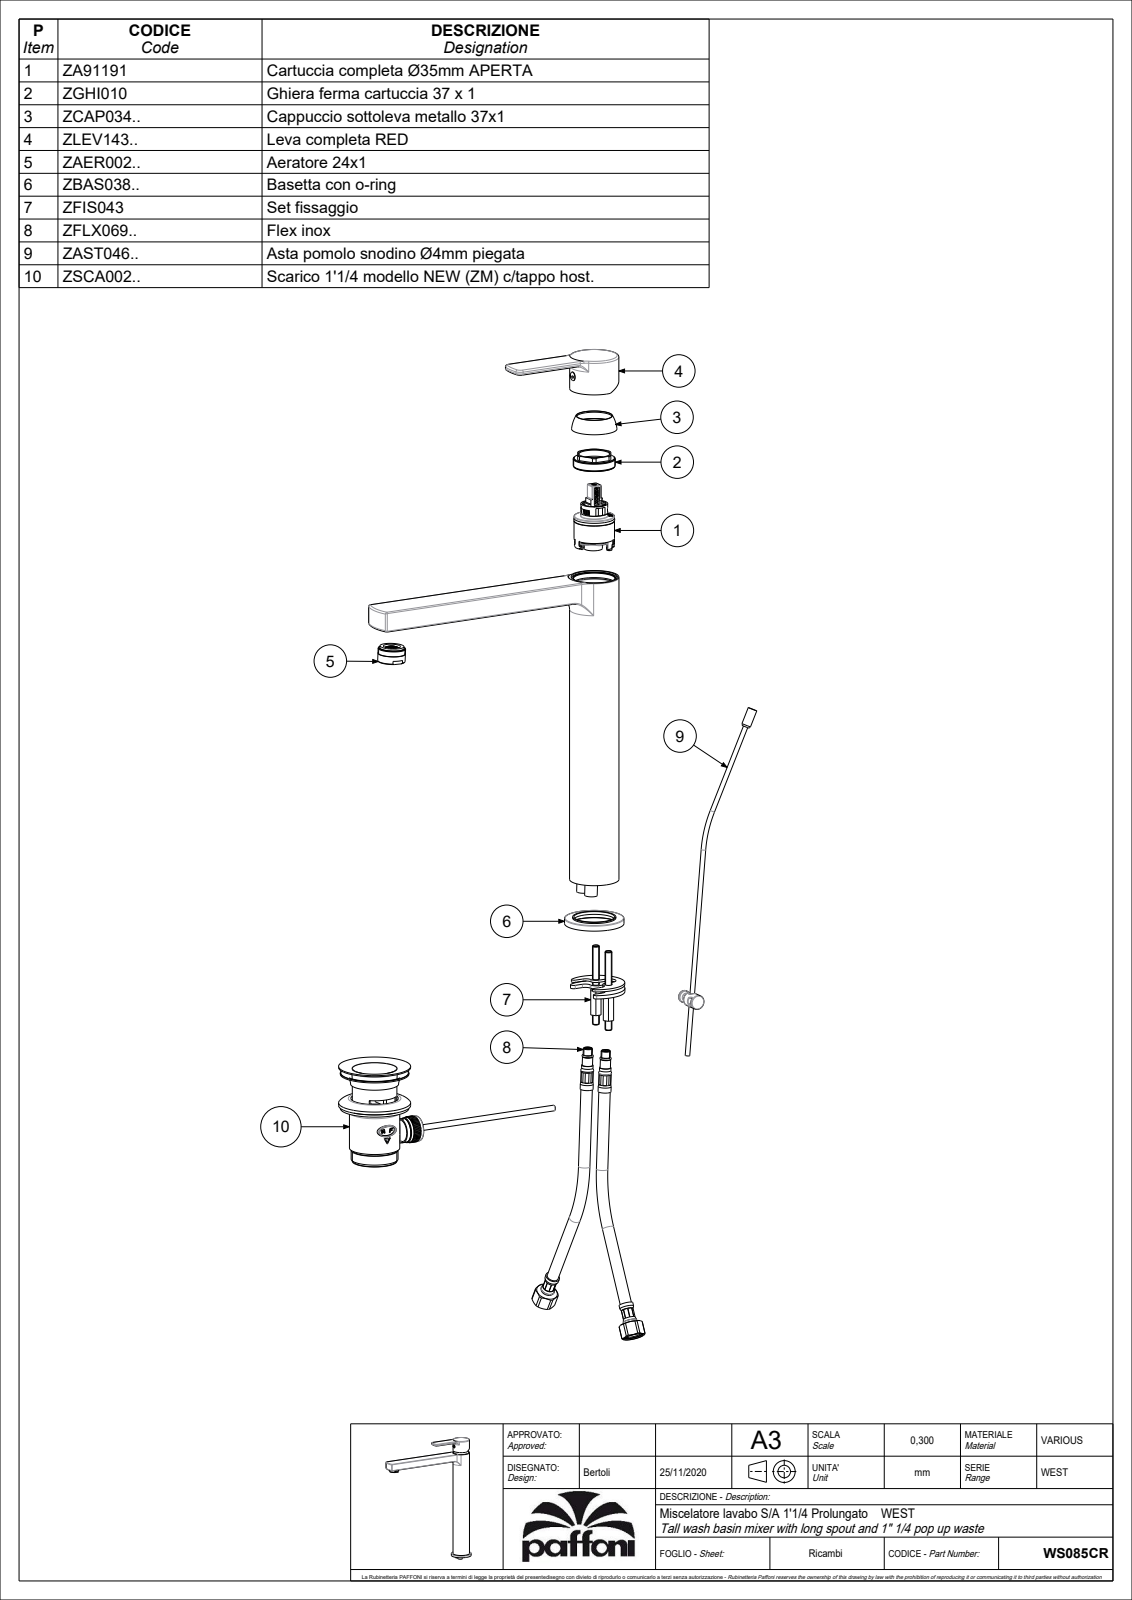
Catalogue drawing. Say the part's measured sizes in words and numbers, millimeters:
The part is named "WS085CR". Its 3-D file was written by "CREO PARAMETRIC BY PTC INC, 2020044 (CONFIG_CONTROL_DESIGN)". It is 7 solids with 3431 faces: 2429 planar, 557 cylindrical and 445 other. Overall it measures 314.78 by 263.5 by 52 millimeters. Its volume is 258 971 cubic millimeters and its surface area 171 608 square millimeters. Round holes: 4 of diameter 6, 3 of diameter 4, 3 of diameter 5, 2 of diameter 5.5, 2 of diameter 6.5, 2 of diameter 8, 2 of diameter 8.2, 1 of diameter 3, 1 of diameter 3.3, 1 of diameter 3.4, 1 of diameter 3.5, 1 of diameter 4.5. Round bosses or shafts: 7 of diameter 8, 3 of diameter 4, 2 of diameter 6, 2 of diameter 4.8, 1 of diameter 52, 1 of diameter 43.2, 1 of diameter 43, 1 of diameter 42.6. Partial cylindrical surfaces (rounded edges, fillets, slot ends): 85 of radius 0.5, 25 of radius 1.5, 17 of radius 1, 6 of radius 1.7, 5 of radius 2, 4 of radius 0.8, 4 of radius 5.8, 3 of radius 12.75. The main face-to-face distances are 3.5, 14.5, 18, 11, 27.5, 31, 48.55, 45.05, 34.05, 30.55. The hole center spacings are 14, 13.6, 2.83, 8.6, 13.45, 15.13, 20.1, 21.93.
